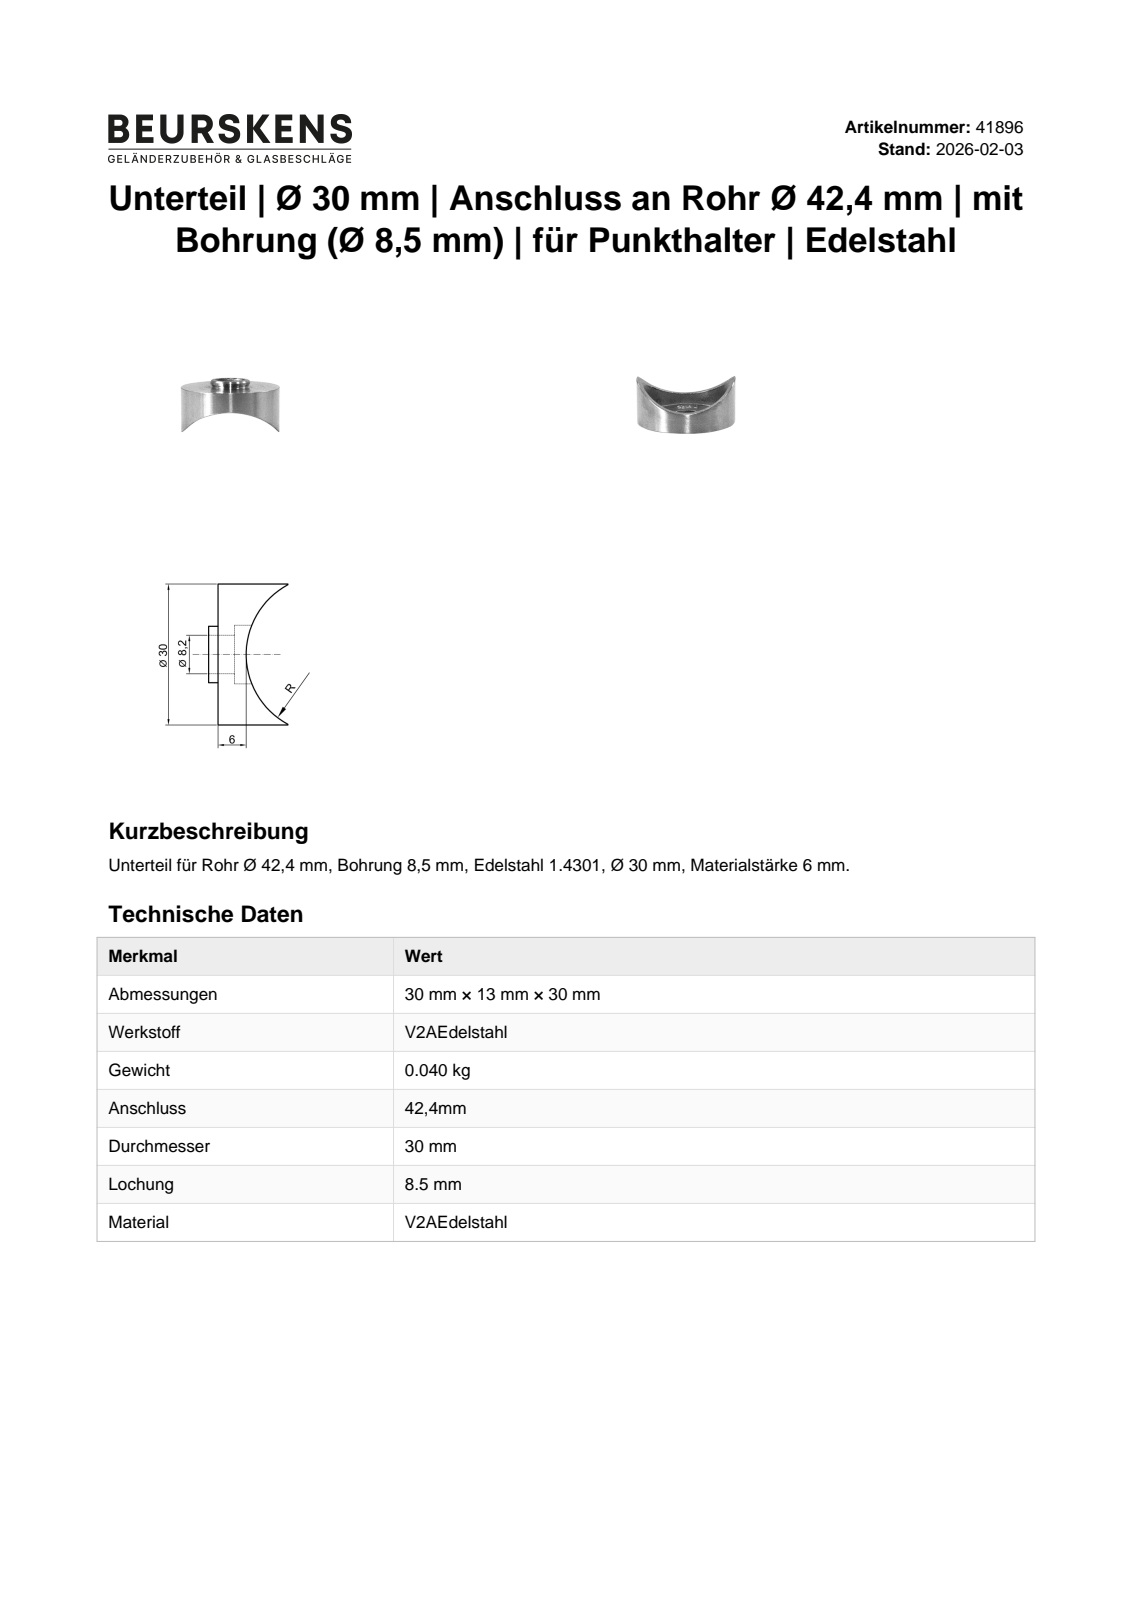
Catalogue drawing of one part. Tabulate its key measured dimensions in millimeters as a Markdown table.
| quantity | value |
| --- | --- |
| part name | 41896 |
| STEP written by | Autodesk Inventor 2023 (AUTOMOTIVE_DESIGN) |
| units | millimeters |
| bodies | 1 solid, 8 faces (3 planar, 5 cylindrical, 0 other) |
| overall size | 30 × 30 × 13.72 |
| volume | 3 406 mm³ |
| surface area | 2 721 mm² |
| round holes (diameter × count) | 8.5 × 1, 24 × 1 |
| round bosses / shafts (diameter × count) | 30 × 1, 12 × 1 |
| partial cylindrical surfaces (radius × count) | 21.2 × 1 |
| main face-to-face distances | 3, 4.5, 1.5 |
